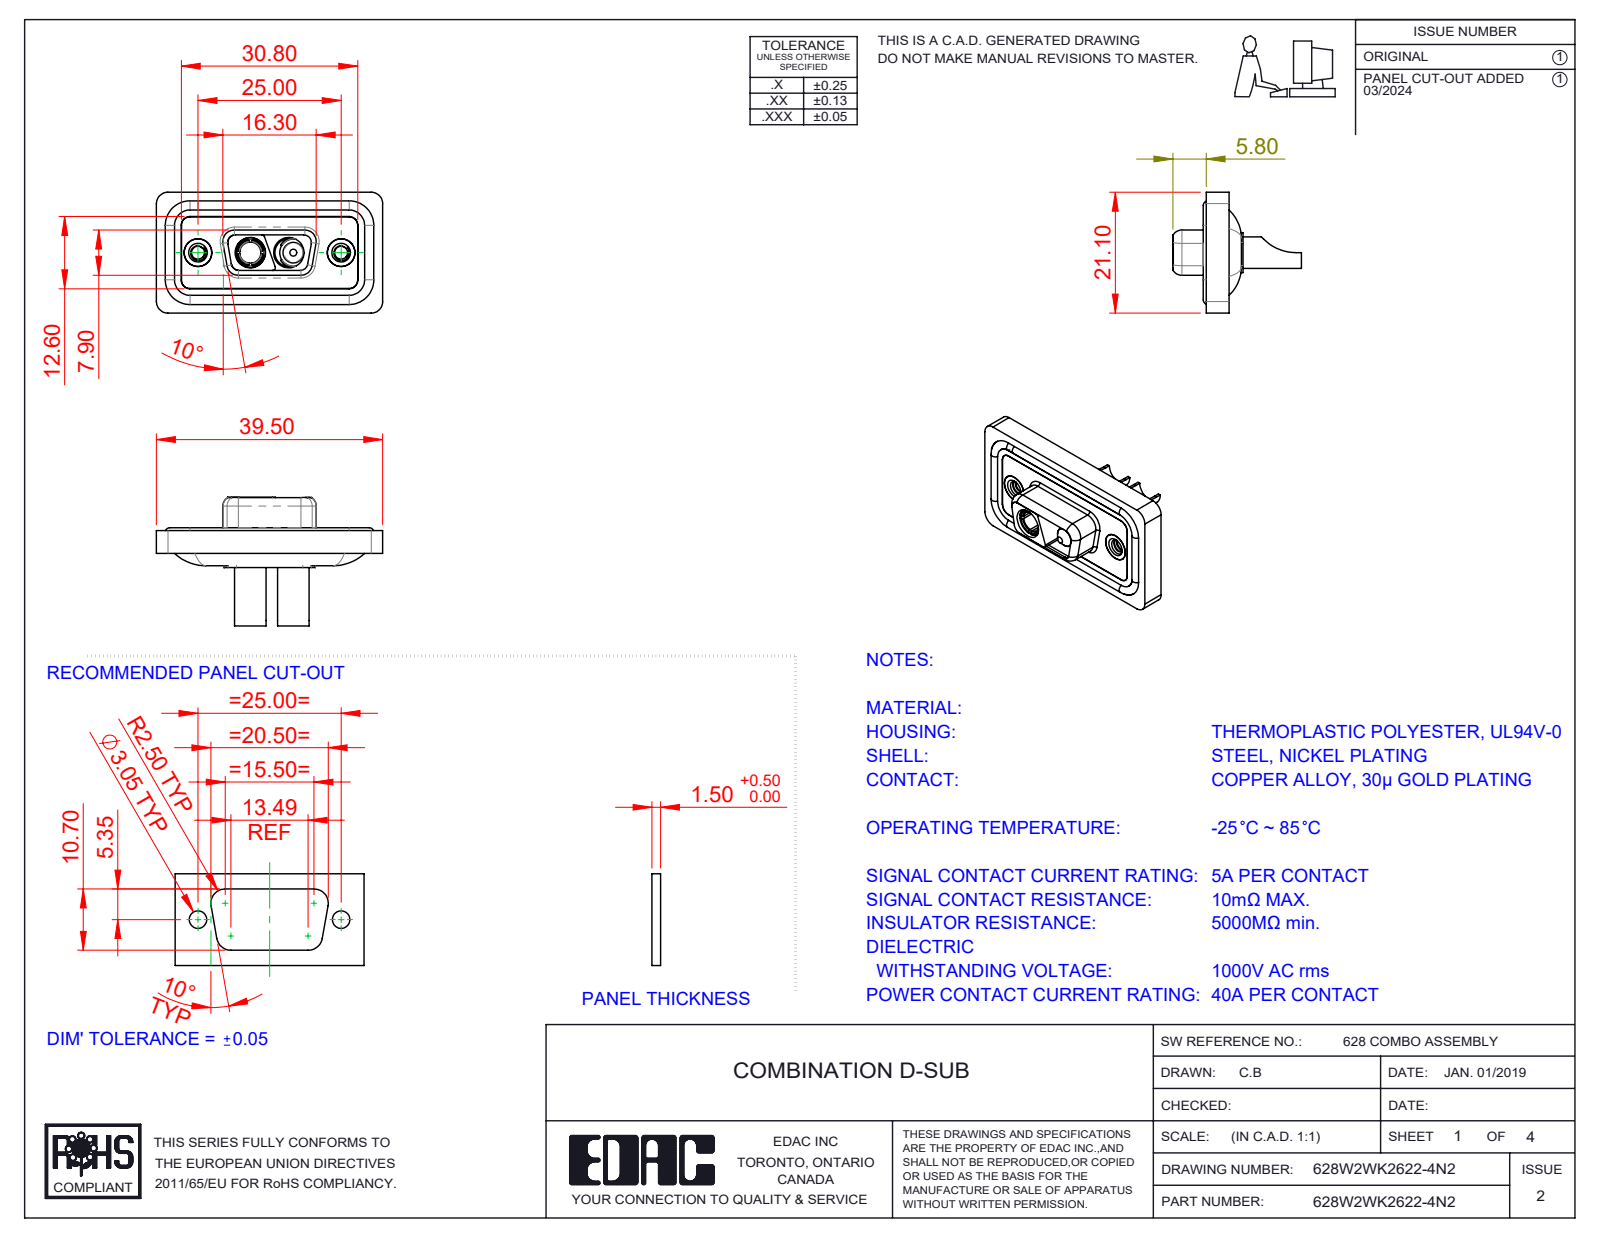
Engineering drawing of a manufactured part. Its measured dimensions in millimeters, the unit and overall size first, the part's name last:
Units: millimetres
Overall size (bounding box): 39.5 × 22.45 × 21.1
Round holes (diameter × count): ⌀4.85 ×4, ⌀2.26 ×2, ⌀4 ×2, ⌀4.05 ×2, ⌀4.6 ×2, ⌀5 ×2, ⌀5.3 ×2, ⌀3.7 ×1
Round bosses / shafts (diameter × count): ⌀1.6 ×4, ⌀5.5 ×2, ⌀5.2 ×2, ⌀4.95 ×2, ⌀4.8 ×2, ⌀4.75 ×2, ⌀3.75 ×2, ⌀4.96 ×1
Partial cylindrical surfaces — rounded edges, fillets, slot ends (radius × count): R1.5 ×22, R2 ×18, R1.35 ×8, R1.6 ×8, R0.5 ×6, R0.25 ×4, R0.6 ×4, R0.65 ×4
Main face-to-face distances: 0.4, 1.1, 2.9, 1.6, 0.5, 1.8, 5.65, 5.35, 3.1, 0.7
Hole centre spacings: 9.14, 15.86, 6.72, 25
Volume: 4 683 mm³ · Surface area: 7 623 mm²
Bodies: 11 solids, 506 faces (148 planar, 233 cylindrical, 125 other)
Part name (STEP PRODUCT): 628W2WK2622-4N2; 628Combo Shell Rear_09 Contacts; 628Combo Threaded Rivet_2; 628Combo Shell Front_09 Contacts (+4 more)
STEP written by: SolidWorks 2023 (CONFIG_CONTROL_DESIGN)
